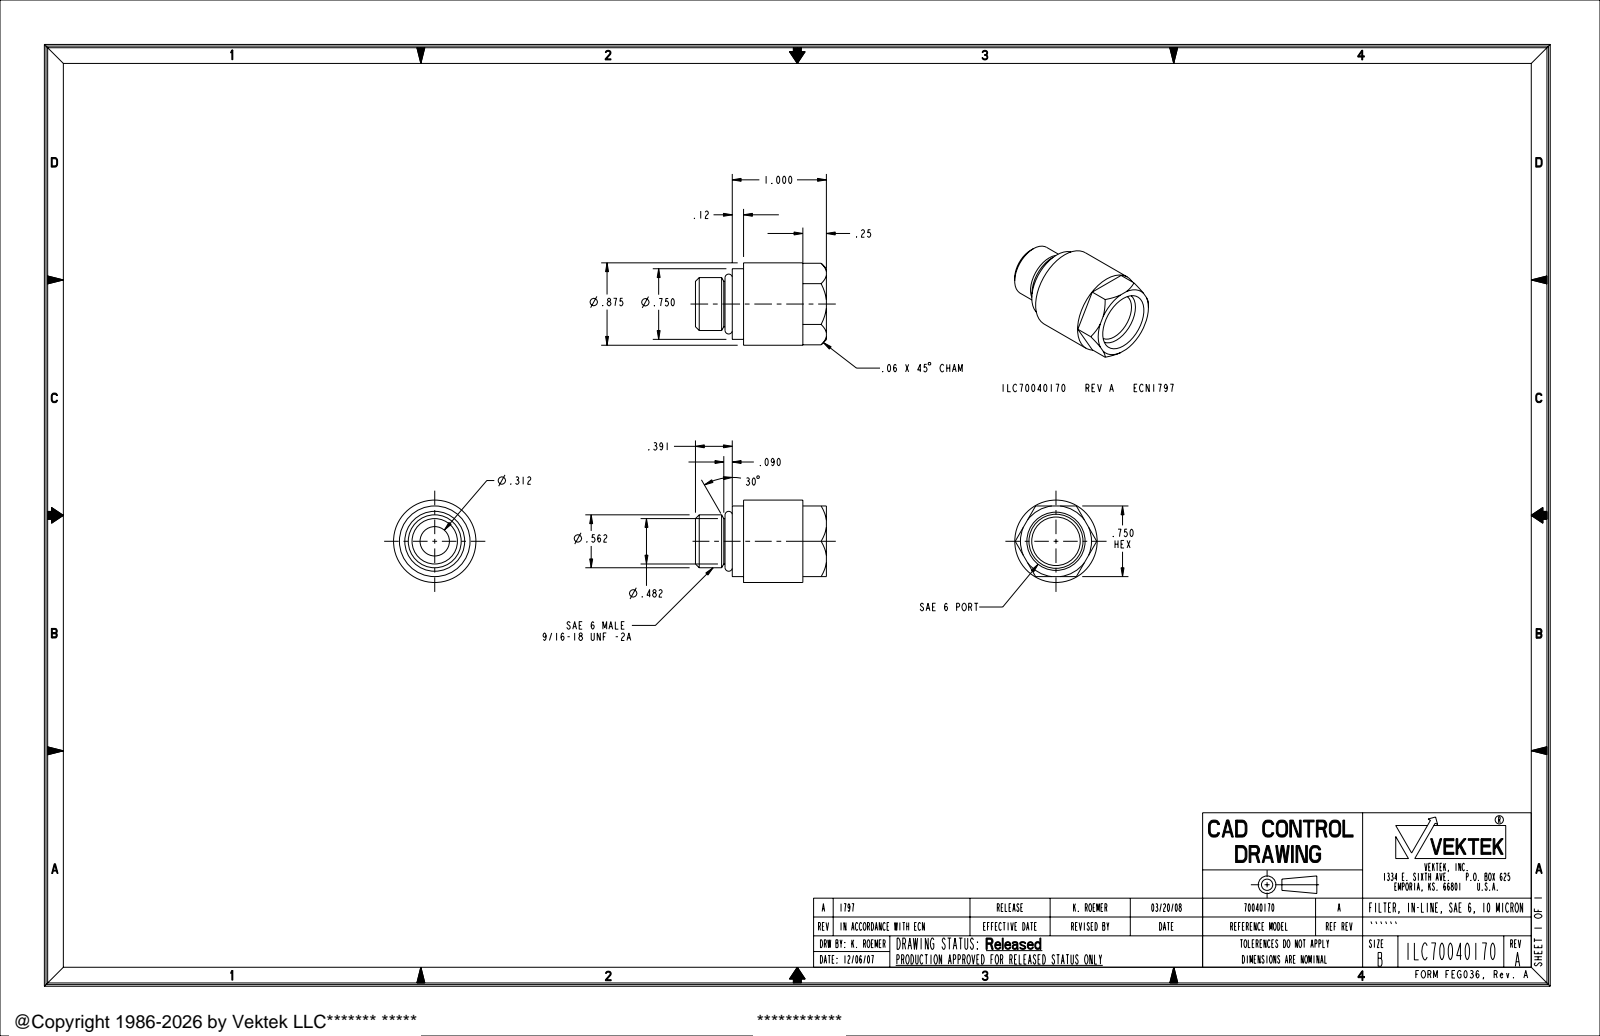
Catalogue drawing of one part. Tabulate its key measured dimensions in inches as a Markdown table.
| quantity | value |
| --- | --- |
| part name | ILC70040170 |
| STEP written by | PRO/ENGINEER BY PARAMETRIC TECHNOLOGY CORPORATION, 2007460 (AUTOMOTIVE_DESIGN_CC2) |
| units | inches |
| bodies | 1 solid, 48 faces (14 planar, 14 cylindrical, 20 other) |
| overall size | 1.391 × 0.875 × 0.875 |
| volume | 0.476 in³ |
| surface area | 6.313 in² |
| round holes (diameter × count) | 0.312 × 1, 0.515 × 1 |
| round bosses / shafts (diameter × count) | 0.875 × 1, 0.75 × 1, 0.562 × 1, 0.482 × 1 |
| main face-to-face distances | 0.391, 0.75, 0.271, 0.12, 1, 0.88, 0.609, 0.75, 0.63, 0.359 |
